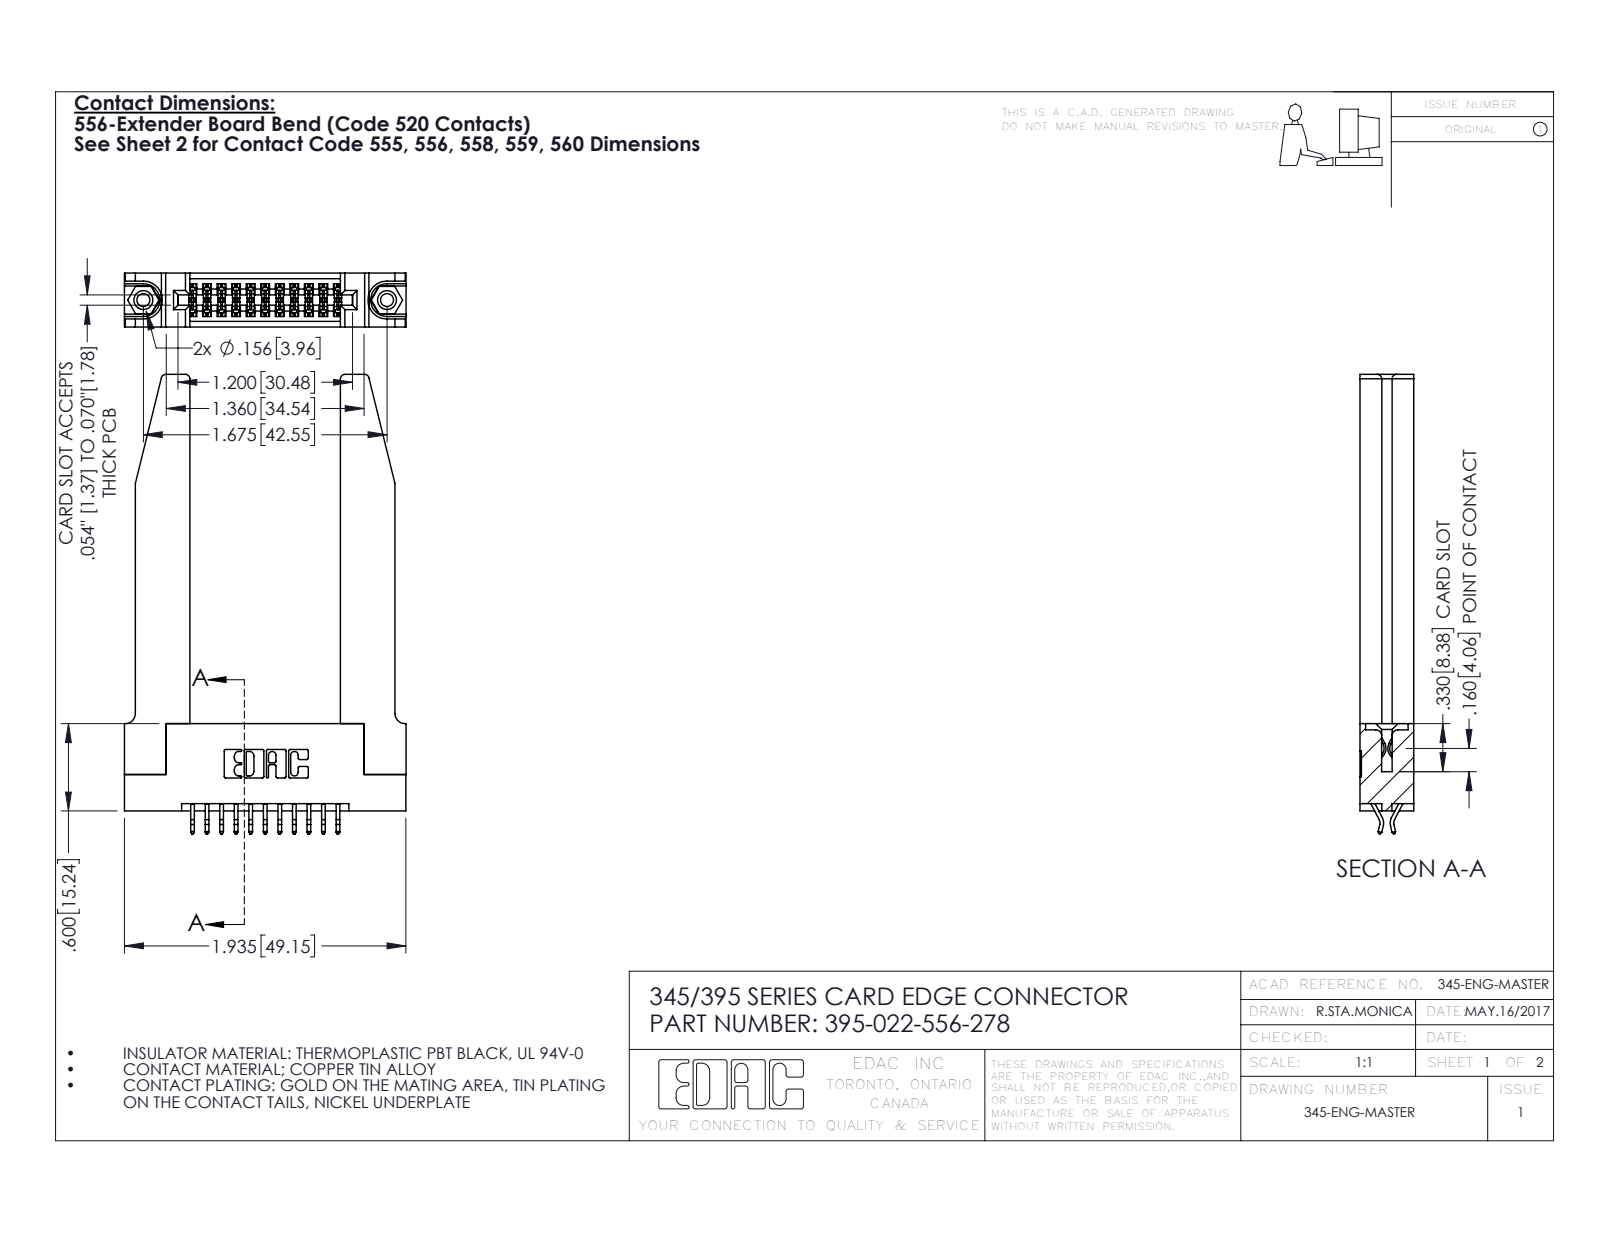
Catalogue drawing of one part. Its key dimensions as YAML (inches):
part_name: "345 Part_Flush Mounting Lugs - 0.156 Dia-TH; 345-292-001_556 Tail; 345-220-078_345-220-078; 395-022-556-278 (+1 more)"
step_written_by: "SolidWorks 2016 (CONFIG_CONTROL_DESIGN)"
units: inches
bodies: {solids: 27, faces: 1592, planar: 1036, cylindrical: 504, other: 52}
overall_size: [3.157, 1.936, 0.37]
volume: 0.748
surface_area: 19.92
round_holes:
  - {diameter: 0.089, count: 2}
  - {diameter: 0.125, count: 2}
  - {diameter: 0.156, count: 2}
  - {diameter: 0.064, count: 1}
round_bosses_or_shafts:
  - {diameter: 0.155, count: 2}
partial_cylinders:
  - {radius: 0.006, count: 33}
  - {radius: 0.01, count: 22}
  - {radius: 0.03, count: 8}
  - {radius: 0.007, count: 6}
  - {radius: 0.031, count: 6}
  - {radius: 0.026, count: 3}
  - {radius: 0.01, count: 2}
  - {radius: 0.014, count: 2}
face_to_face_distances: [0.37, 0.072, 0.298, 0.2, 0.148, 0.15, 0.077, 0.22, 1.035, 0.025]
hole_center_spacings: [0.27, 1.443, 1.675]
